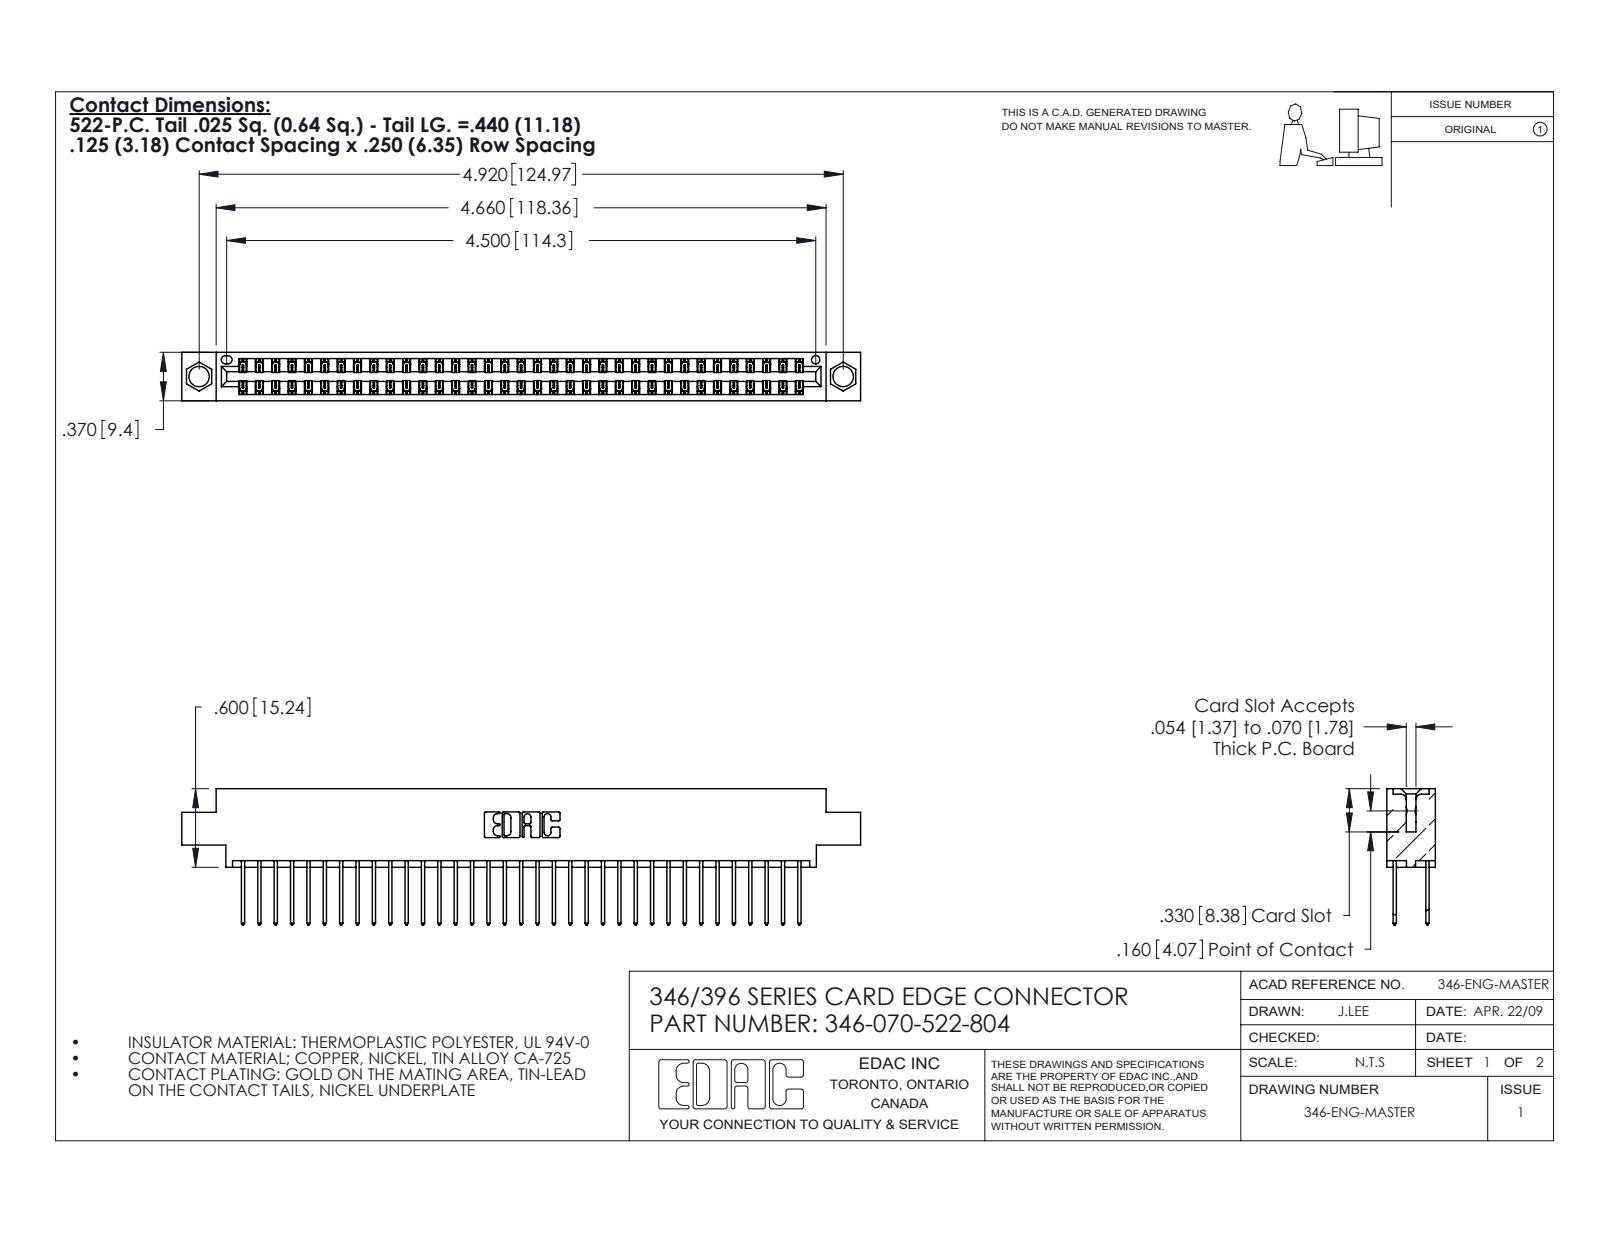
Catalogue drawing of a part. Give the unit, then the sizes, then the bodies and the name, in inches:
Units: inches
Overall size (bounding box): 5.185 × 1.04 × 0.37
Round holes (diameter × count): ⌀0.156 ×2, ⌀0.064 ×1
Partial cylindrical surfaces — rounded edges, fillets, slot ends (radius × count): R0.006 ×105, R0.01 ×70, R0.01 ×22, R0.007 ×6, R0.031 ×6, R0.026 ×3, R0.014 ×2, R0.022 ×2
Main face-to-face distances: 0.048, 0.322, 0.25, 0.37, 0.072, 0.298, 0.025, 0.275, 0.222, 0.148
Hole centre spacings: 0.246, 4.711, 4.92
Volume: 0.775 in³ · Surface area: 28.23 in²
Bodies: 71 solids, 3780 faces (2544 planar, 1236 cylindrical, 0 other)
Part name (STEP PRODUCT): 345-292-001_345-293-122; 346-070-522-804; 346 Part_0.170 Offset - 0.156 Dia-TH
STEP written by: SolidWorks 2020 (CONFIG_CONTROL_DESIGN)
